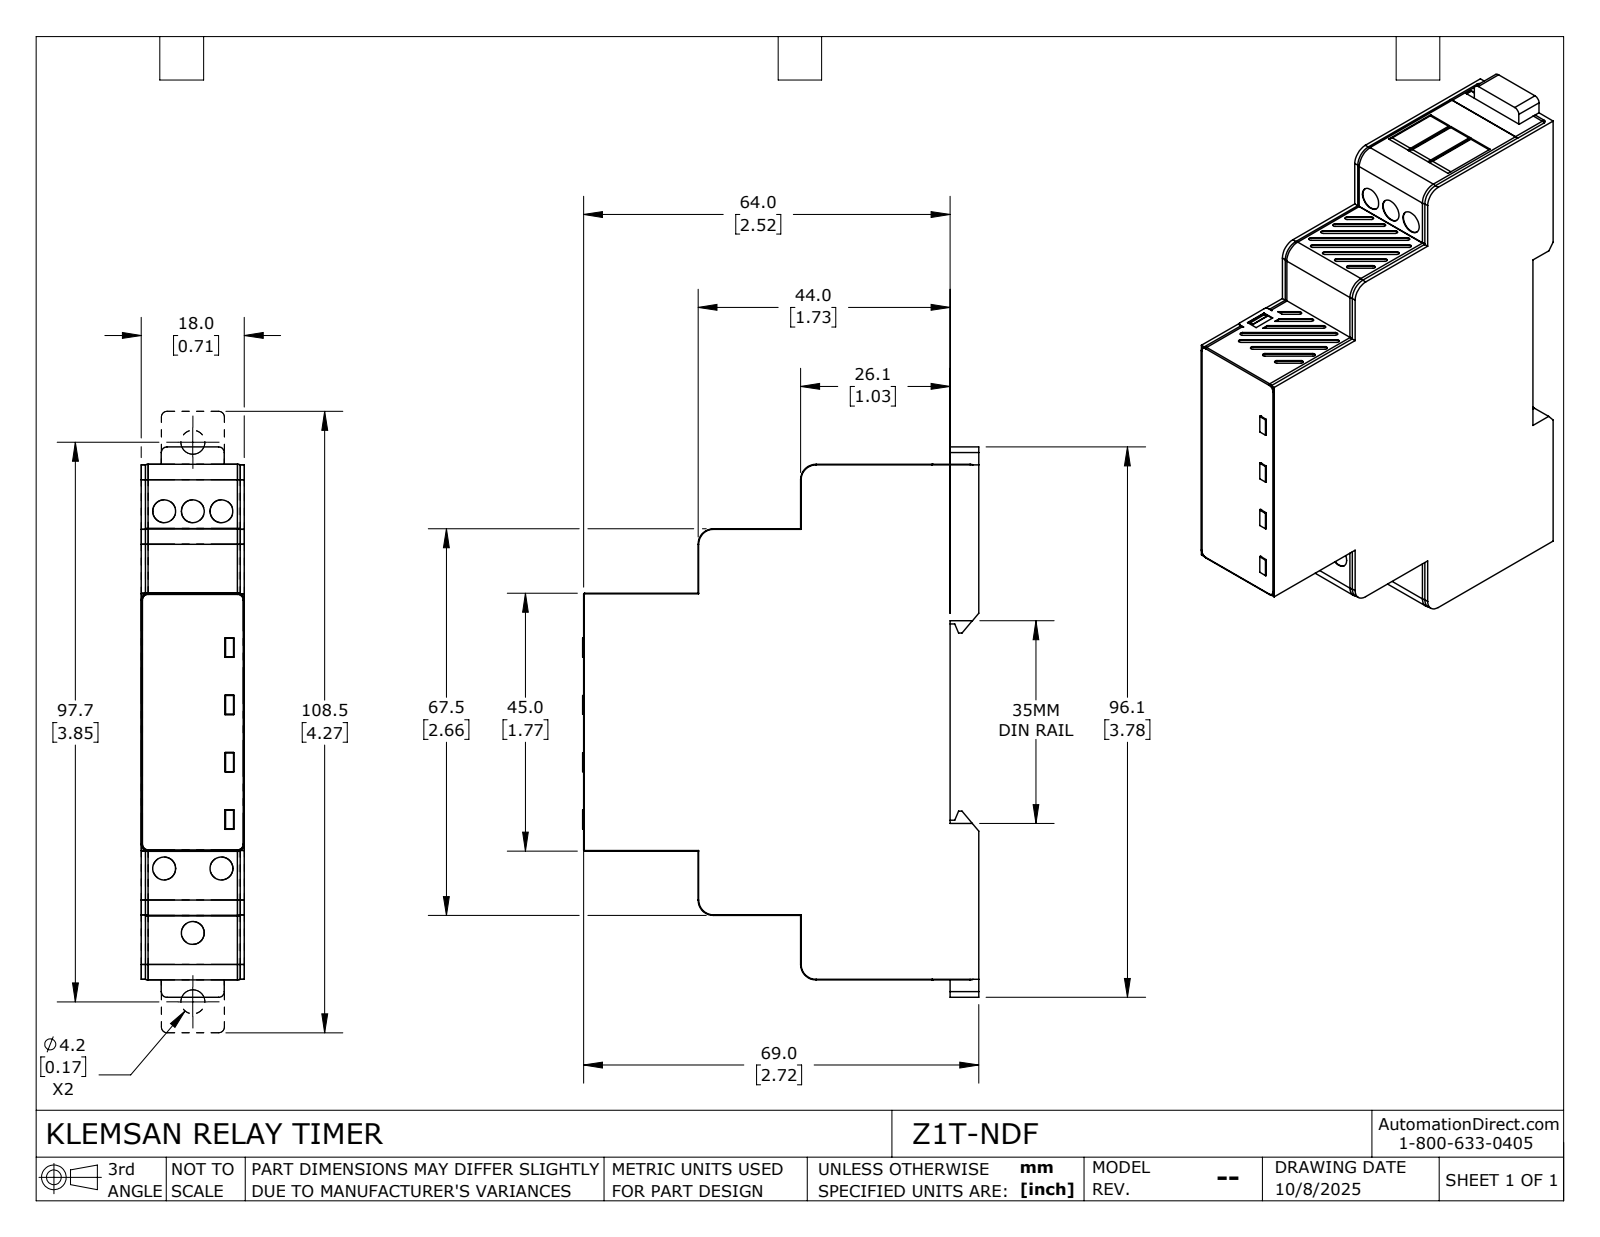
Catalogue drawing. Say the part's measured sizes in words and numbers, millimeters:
The part is named "Z1T-NDF". Its 3-D file was written by "SolidWorks 2024 (CONFIG_CONTROL_DESIGN)". It is 3 solids with 440 faces: 280 planar, 60 cylindrical and 100 other. Overall it measures 96.07 by 69.15 by 18 millimeters. Its volume is 83 847 cubic millimeters and its surface area 17 884 square millimeters. Round holes: 2 of diameter 4.2, 1 of diameter 4. Partial cylindrical surfaces (rounded edges, fillets, slot ends): 16 of radius 1.2, 4 of radius 0.2, 4 of radius 1, 4 of radius 2.6, 4 of radius 2.7, 2 of radius 0.5, 2 of radius 1.5. The main face-to-face distances are 18, 3.5, 14.5, 11.25, 64, 5, 69, 22.5, 67.4, 67.5. The hole center spacings are 5.83, 79.43, 85.26.
